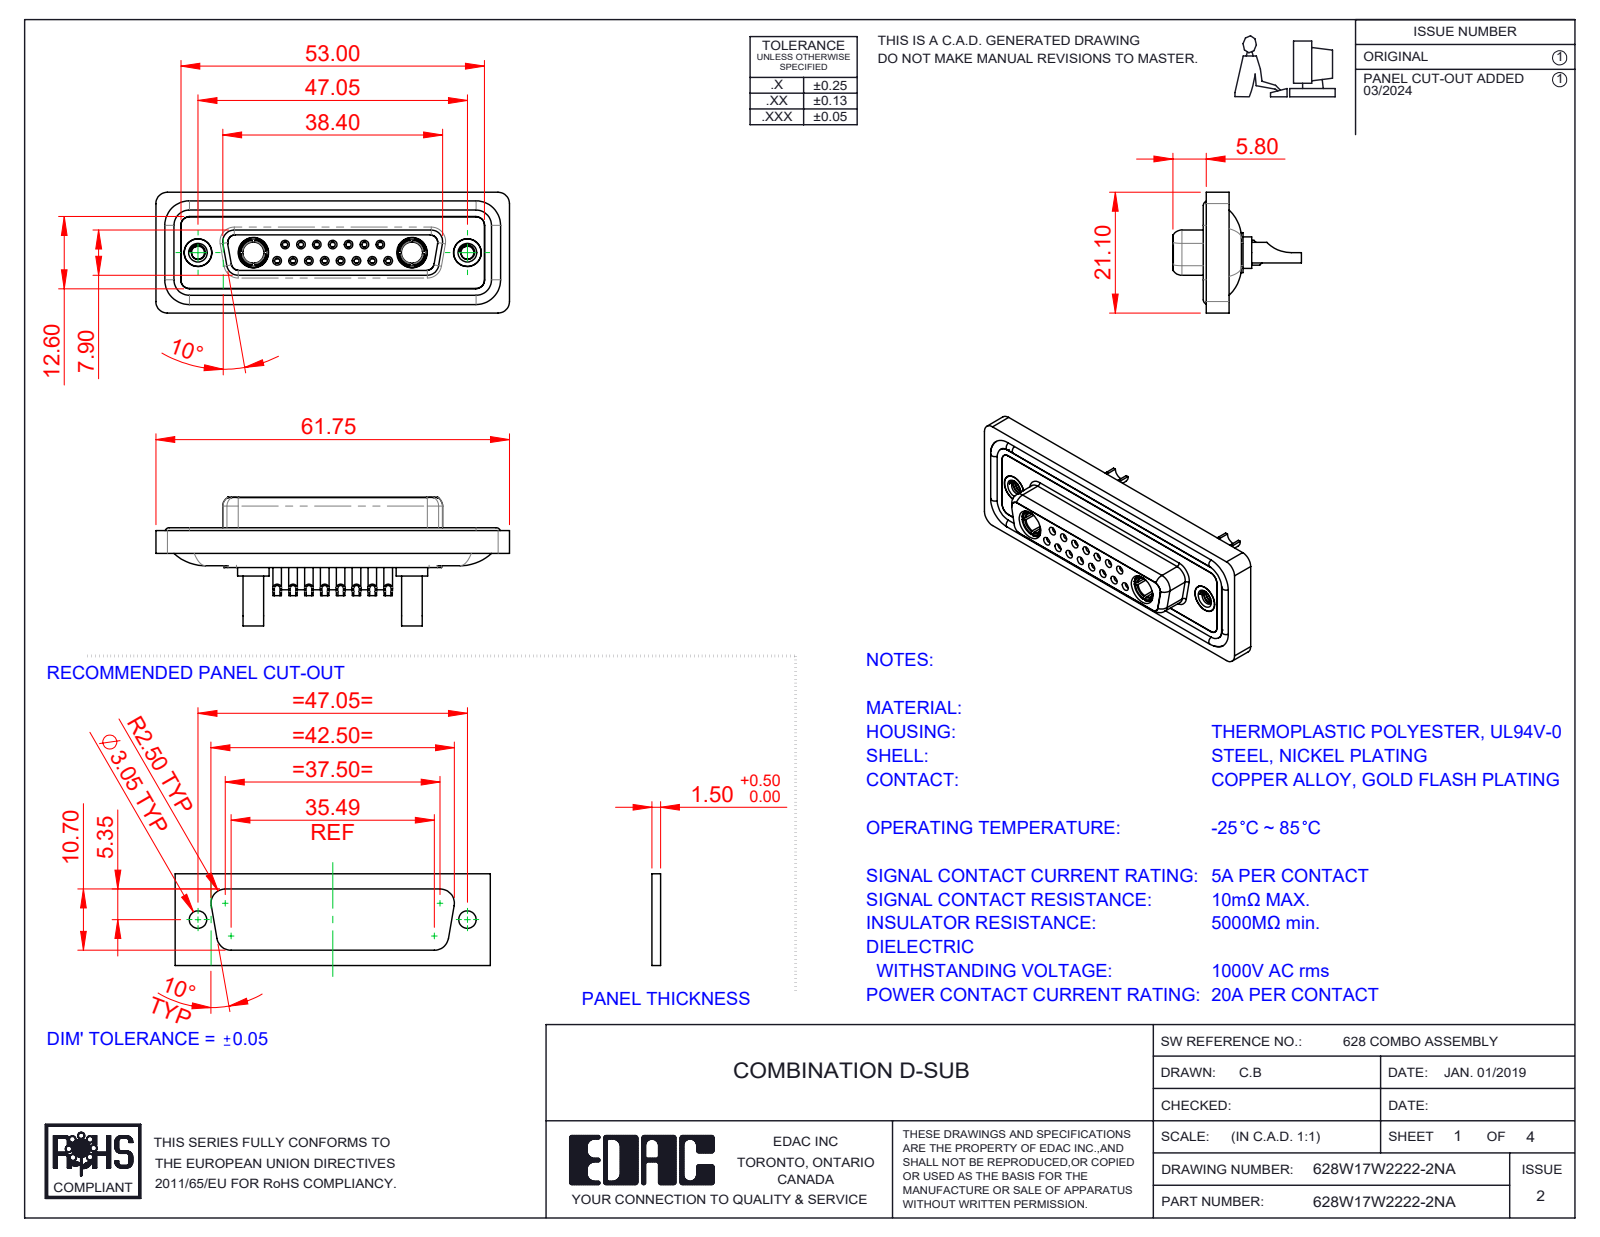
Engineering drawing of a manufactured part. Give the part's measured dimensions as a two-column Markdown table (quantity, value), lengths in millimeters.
| quantity | value |
| --- | --- |
| part name | Power Socket_20A SC; 628Combo Housing_17W2; 628Combo Contact Row 1_22; 628Combo Waterproof Housing_25 Contacts (+5 more) |
| STEP written by | SolidWorks 2023 (CONFIG_CONTROL_DESIGN) |
| units | millimeters |
| bodies | 26 solids, 1369 faces (424 planar, 557 cylindrical, 388 other) |
| overall size | 61.75 × 22.45 × 21.1 |
| volume | 8 383 mm³ |
| surface area | 14 178 mm² |
| round holes (diameter × count) | 0.9 × 15, 1 × 15, 1.1 × 15, 1.5 × 15, 2 × 15, 1.6 × 8, 1.7 × 7, 4.85 × 4, 2.26 × 2, 2.7 × 2, 3.7 × 2, 4 × 2 |
| round bosses / shafts (diameter × count) | 2.2 × 15, 1.6 × 11, 5.5 × 2, 5.2 × 2, 4.96 × 2, 4.95 × 2, 4.8 × 2, 4.75 × 2 |
| partial cylindrical surfaces (radius × count) | 1.5 × 22, 2 × 18, 1.35 × 8, 1.6 × 8, 1 × 6, 0.25 × 4, 0.5 × 4, 0.6 × 4 |
| main face-to-face distances | 0.4, 1.8, 7.45, 5.65, 6.6, 0.5, 7.05, 1.6, 2.9, 1.1 |
| hole center spacings | 3.16, 2.77, 8.31, 5.54, 5.03, 5.04, 7.49, 11.08 |
